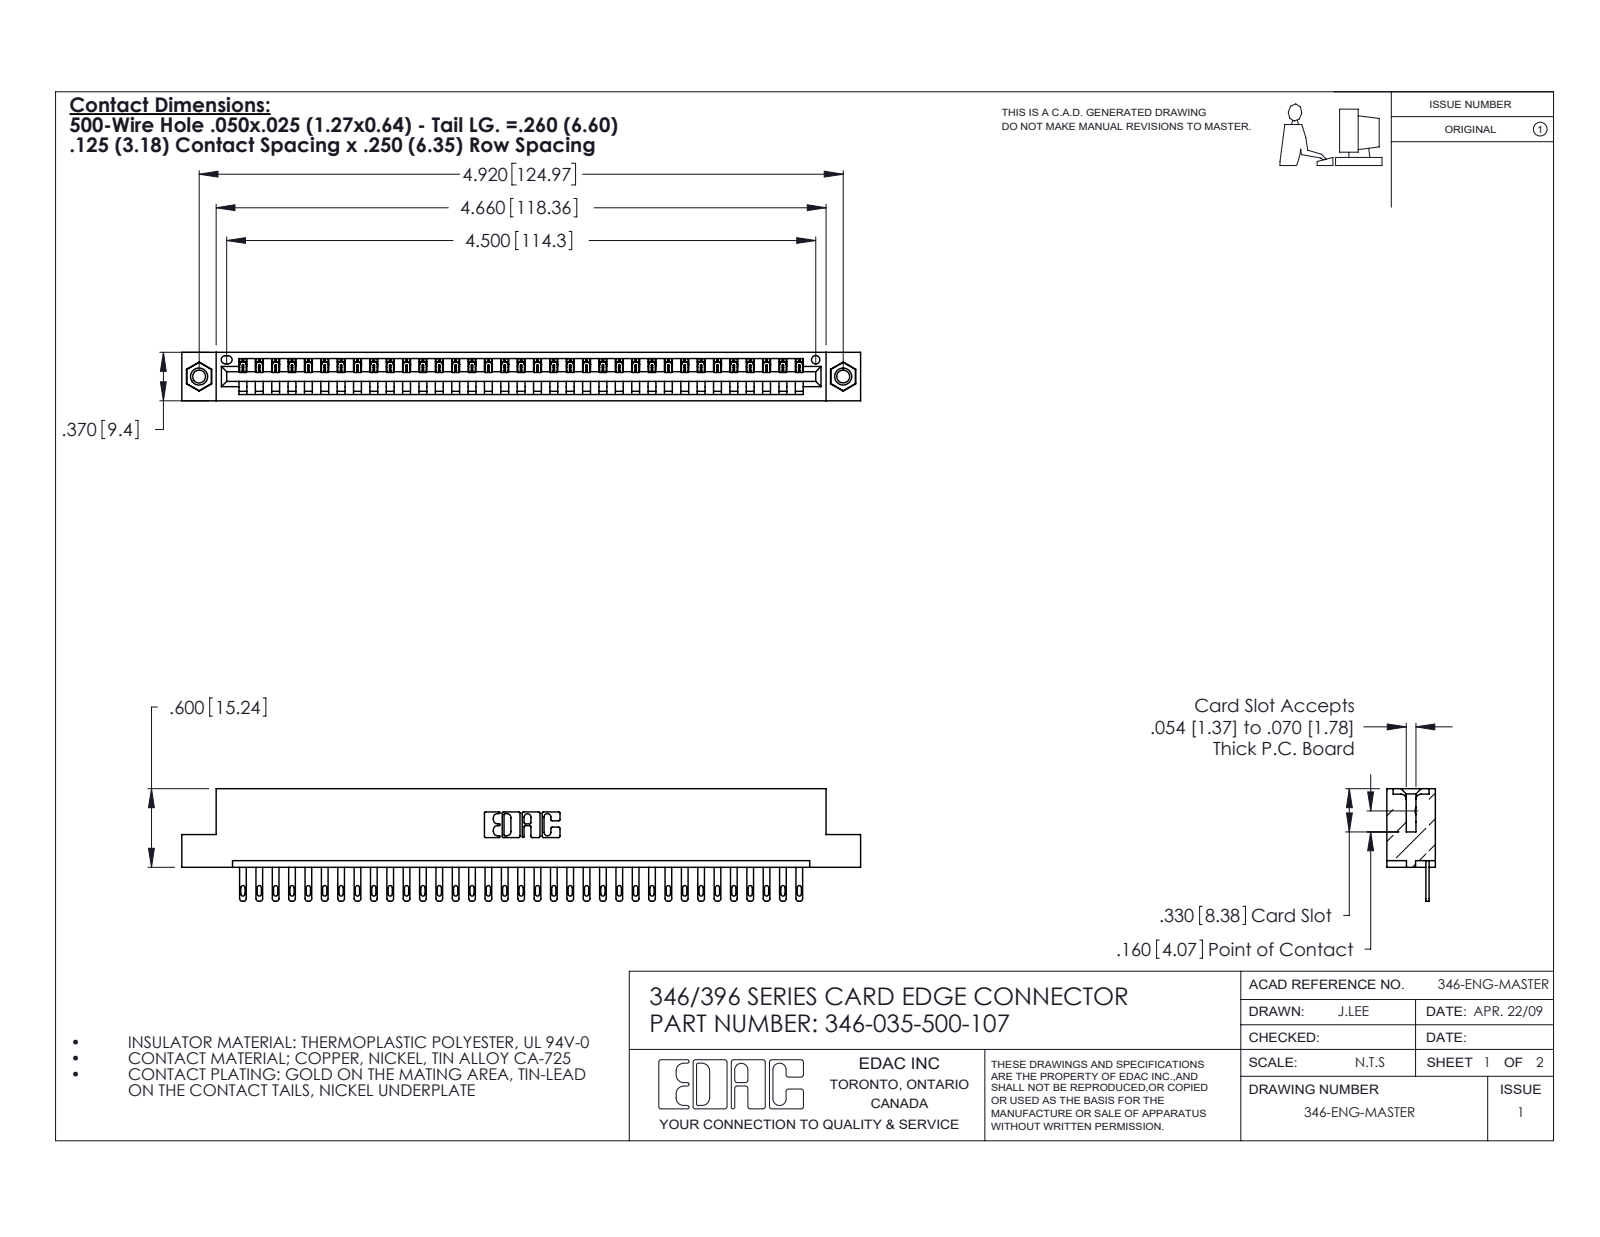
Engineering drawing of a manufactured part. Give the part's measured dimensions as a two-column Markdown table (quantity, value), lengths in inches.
| quantity | value |
| --- | --- |
| part name | 346 Part_Flush Mounting Lugs - 0.156 Dia-TI; 345-250-001_345-250-005-103; 345-292-001_345-293-100; 346-035-500-107 |
| STEP written by | SolidWorks 2020 (CONFIG_CONTROL_DESIGN) |
| units | inches |
| bodies | 38 solids, 2072 faces (1298 planar, 758 cylindrical, 16 other) |
| overall size | 5.185 × 0.86 × 0.37 |
| volume | 0.767 in³ |
| surface area | 24.41 in² |
| round holes (diameter × count) | 0.098 × 2, 0.125 × 2, 0.156 × 2, 0.064 × 1 |
| round bosses / shafts (diameter × count) | 0.155 × 2 |
| partial cylindrical surfaces (radius × count) | 0.006 × 70, 0.016 × 70, 0.02 × 70, 0.01 × 22, 0.007 × 6, 0.031 × 6, 0.026 × 3, 0.031 × 2 |
| main face-to-face distances | 0.048, 0.322, 0.37, 0.25, 0.072, 0.298, 0.025, 0.148, 0.222, 0.1 |
| hole center spacings | 0.246, 4.711, 4.92 |
